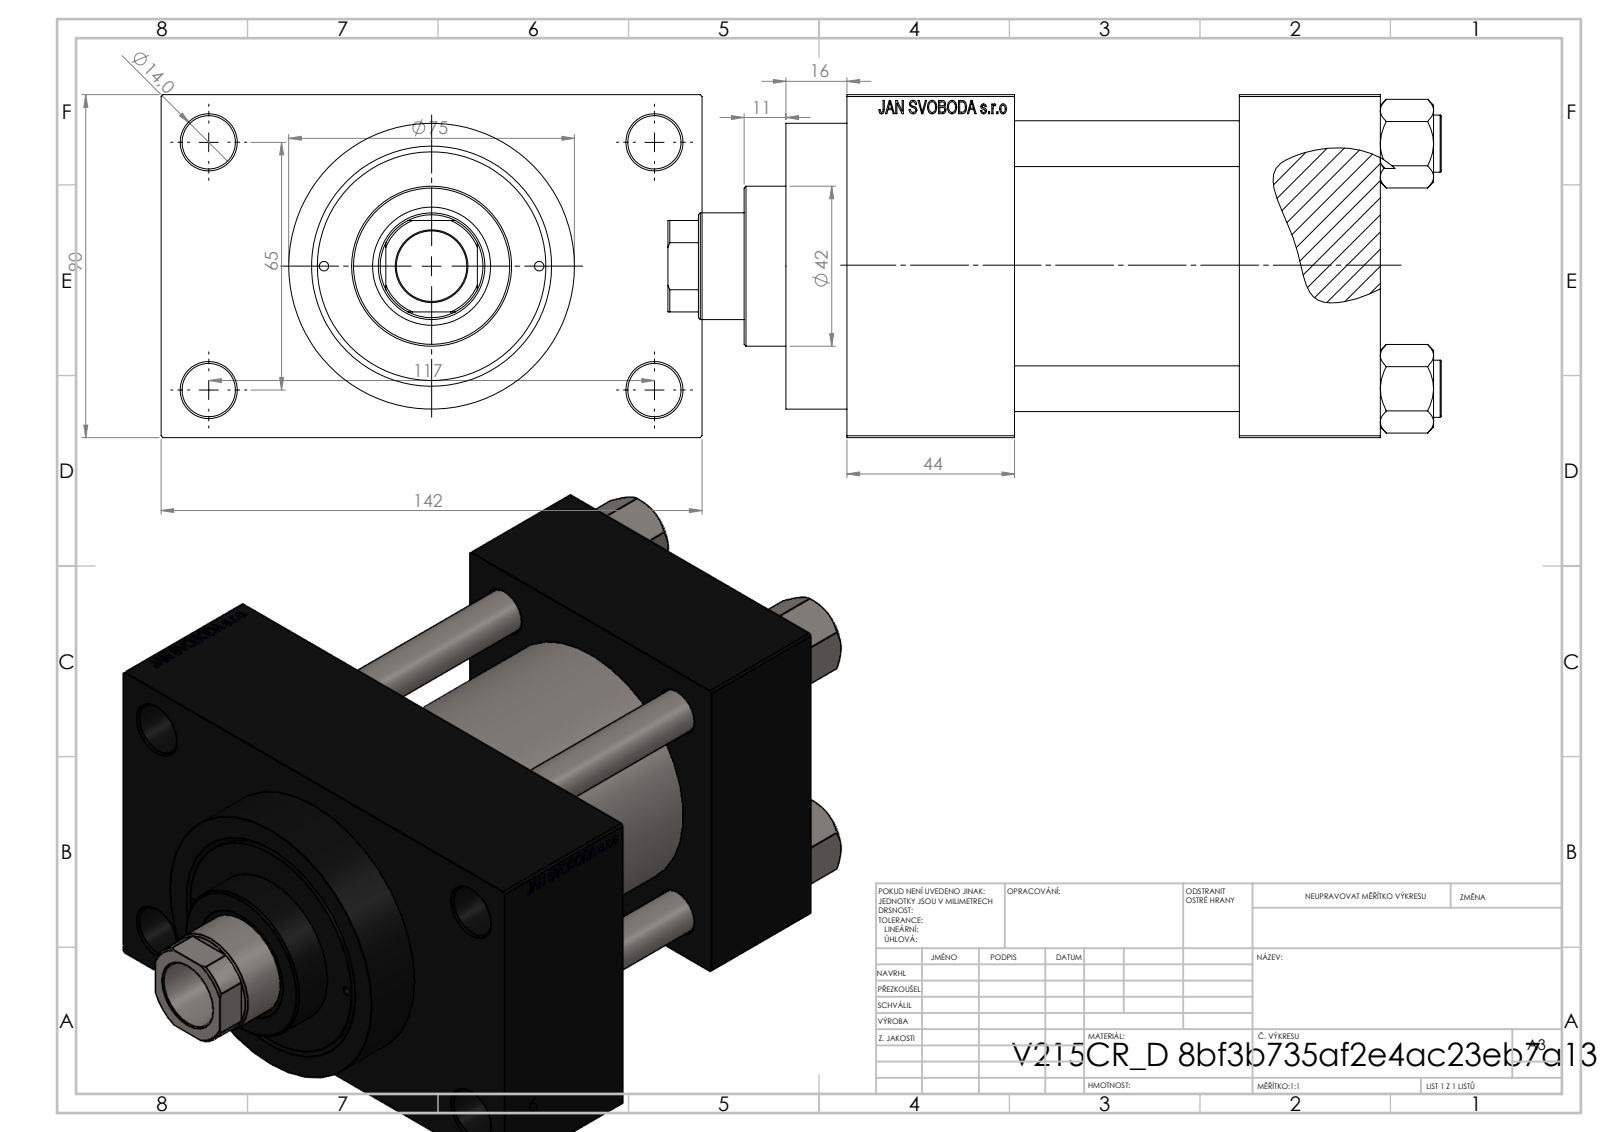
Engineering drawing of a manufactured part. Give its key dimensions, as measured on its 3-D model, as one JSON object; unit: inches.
{"part_name": "V215CR_D_Body; V215CR_VCP_D; V215_VC_A; NUT_M5_D (+1 more)", "step_written_by": "SolidWorks 2019 (CONFIG_CONTROL_DESIGN)", "units": "inches", "bodies": {"solids": 11, "faces": 1111, "planar": 499, "cylindrical": 92, "other": 520}, "overall_size": [7.992, 5.591, 3.543], "volume_in3": 66.88, "surface_area_in2": 310.4, "round_holes": [[0.472, 4], [0.551, 4], [0.098, 2], [0.276, 2], [0.825, 2], [1.181, 2], [0.728, 1], [1.102, 1], [1.22, 1], [1.969, 1], [2.362, 1], [2.48, 1]], "round_bosses_or_shafts": [[0.591, 4], [2.953, 1], [2.717, 1], [1.654, 1]], "partial_cylinders_radius": [[0.531, 1]], "face_to_face_distances": [3.543, 2.323, 1.457, 3.78, 5.512, 4.055, 1.732, 1.024, 4.567, 0.63], "hole_center_spacings": [1.037, 1.275, 1.748, 1.79, 2.531, 2.635, 2.694, 2.748]}
